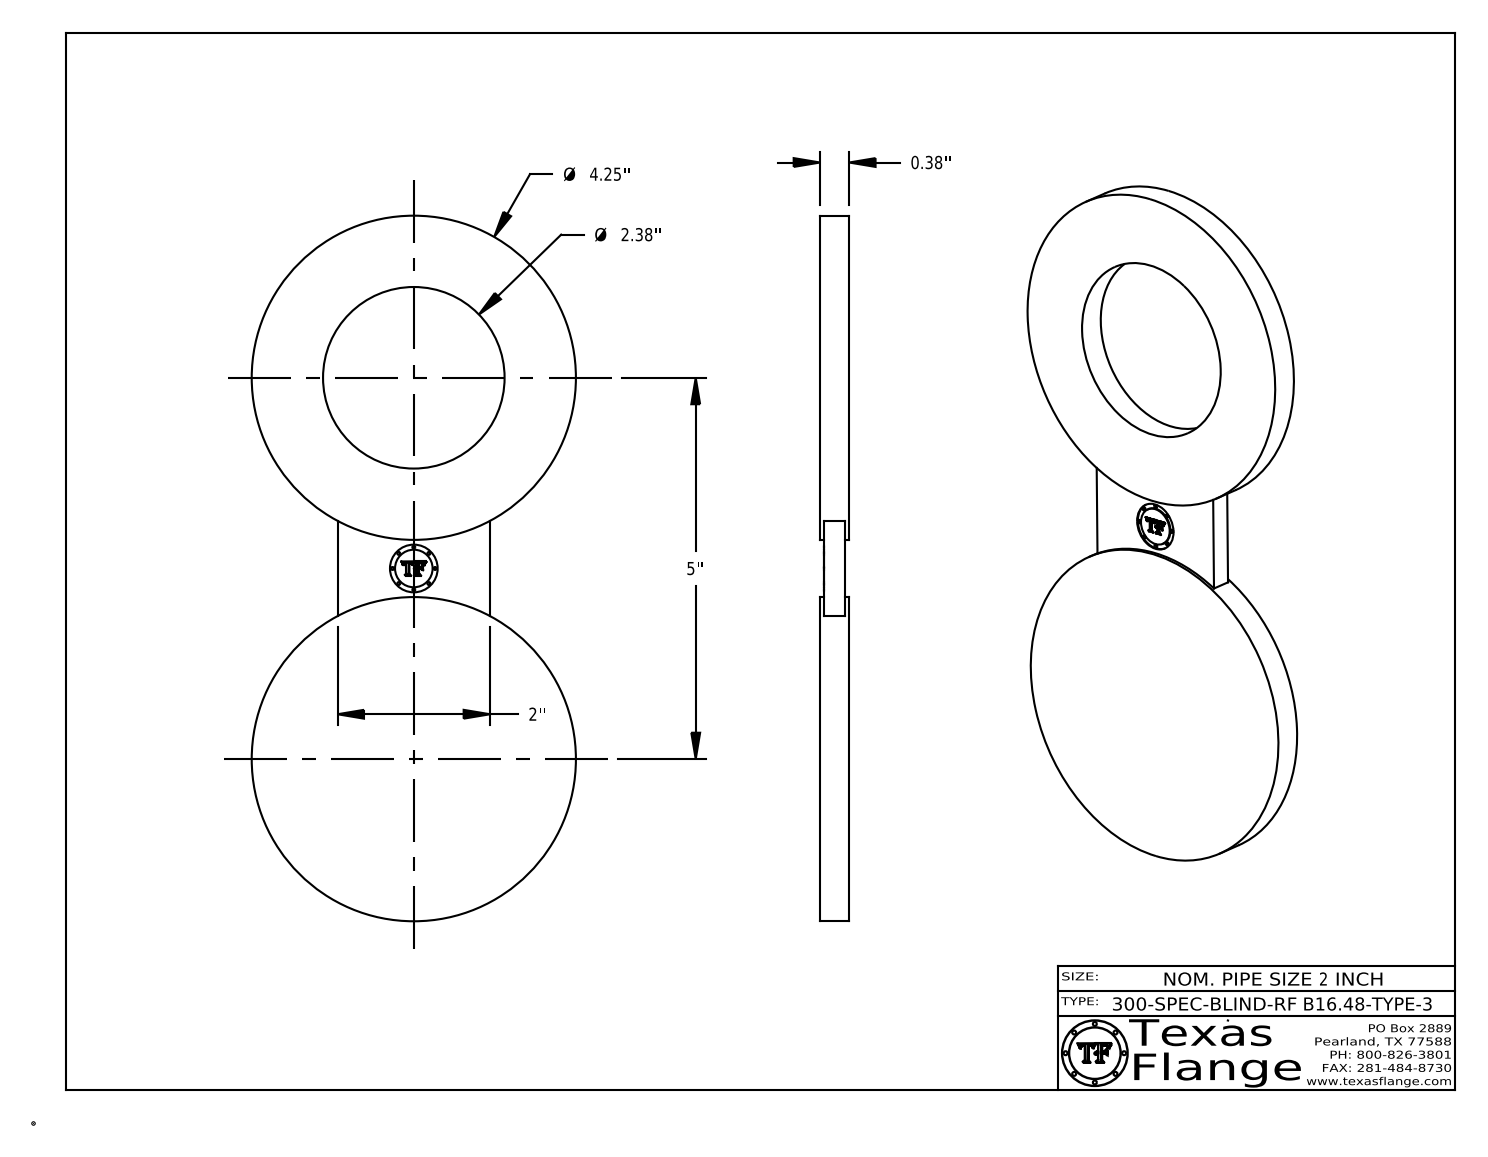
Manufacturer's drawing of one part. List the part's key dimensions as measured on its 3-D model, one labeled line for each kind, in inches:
Part name (STEP PRODUCT): 2-300-SPEC-BLIND-RF-B16.48-TYPE-3
STEP written by: CATIA V5 STEP AP214 (AUTOMOTIVE_DESIGN)
Units: inches
Bodies: 1 solid, 399 faces (373 planar, 26 cylindrical, 0 other)
Overall size (bounding box): 9.25 × 4.25 × 0.38
Volume: 9.609 in³ · Surface area: 64.13 in²
Round holes (diameter × count): ⌀0.625 ×1, ⌀2.38 ×1
Round bosses / shafts (diameter × count): ⌀0.038 ×8, ⌀4.25 ×2, ⌀0.492 ×1
Main face-to-face distances: 0.38, 0.048, 0.333, 0.285, 2, 0.318, 0.27, 0.015, 0.063, 0.937
Hole centre spacings: 2.5
